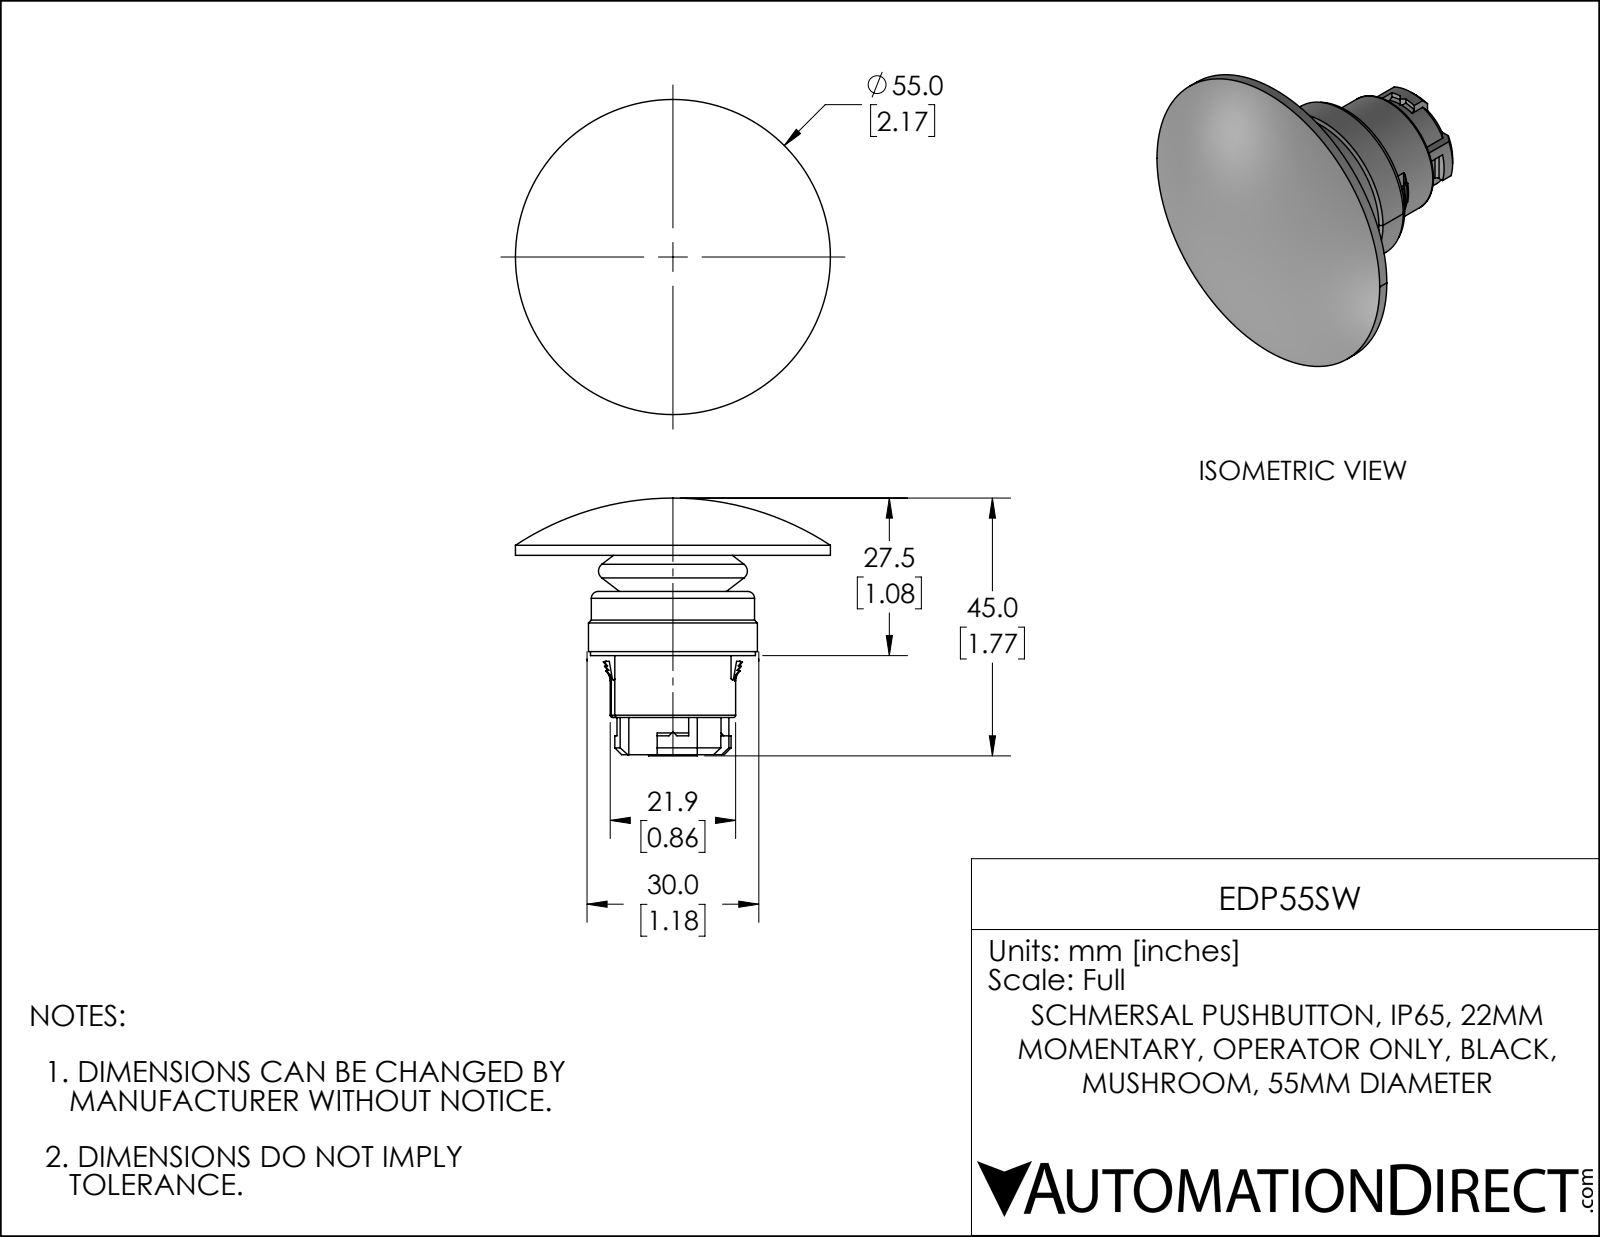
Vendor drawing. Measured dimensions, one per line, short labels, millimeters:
name: EDP55____SW0002
written by: CREO PARAMETRIC BY PTC INC, 2019444 (CONFIG_CONTROL_DESIGN)
unit: mm
bodies: 1 solid, 180 faces (73 planar, 50 cylindrical, 57 other)
size: 55 × 55 × 45
volume: 27 317 mm³; area: 11 167 mm²
holes: 1× ⌀12.15, 1× ⌀19.5, 1× ⌀32
bosses: 1× ⌀55, 1× ⌀29.5, 1× ⌀28.8, 1× ⌀28.5, 1× ⌀21.9, 1× ⌀20, 1× ⌀18.2, 1× ⌀8.5
rounds: 4× R0.2, 2× R0.4, 1× R4.12, 1× R5, 1× R8.8, 1× R10.15, 1× R10.9
face distances: 17.5, 11.2, 6.3, 17.3, 28.5, 34.8, 6.5, 10.8, 22, 28.3
